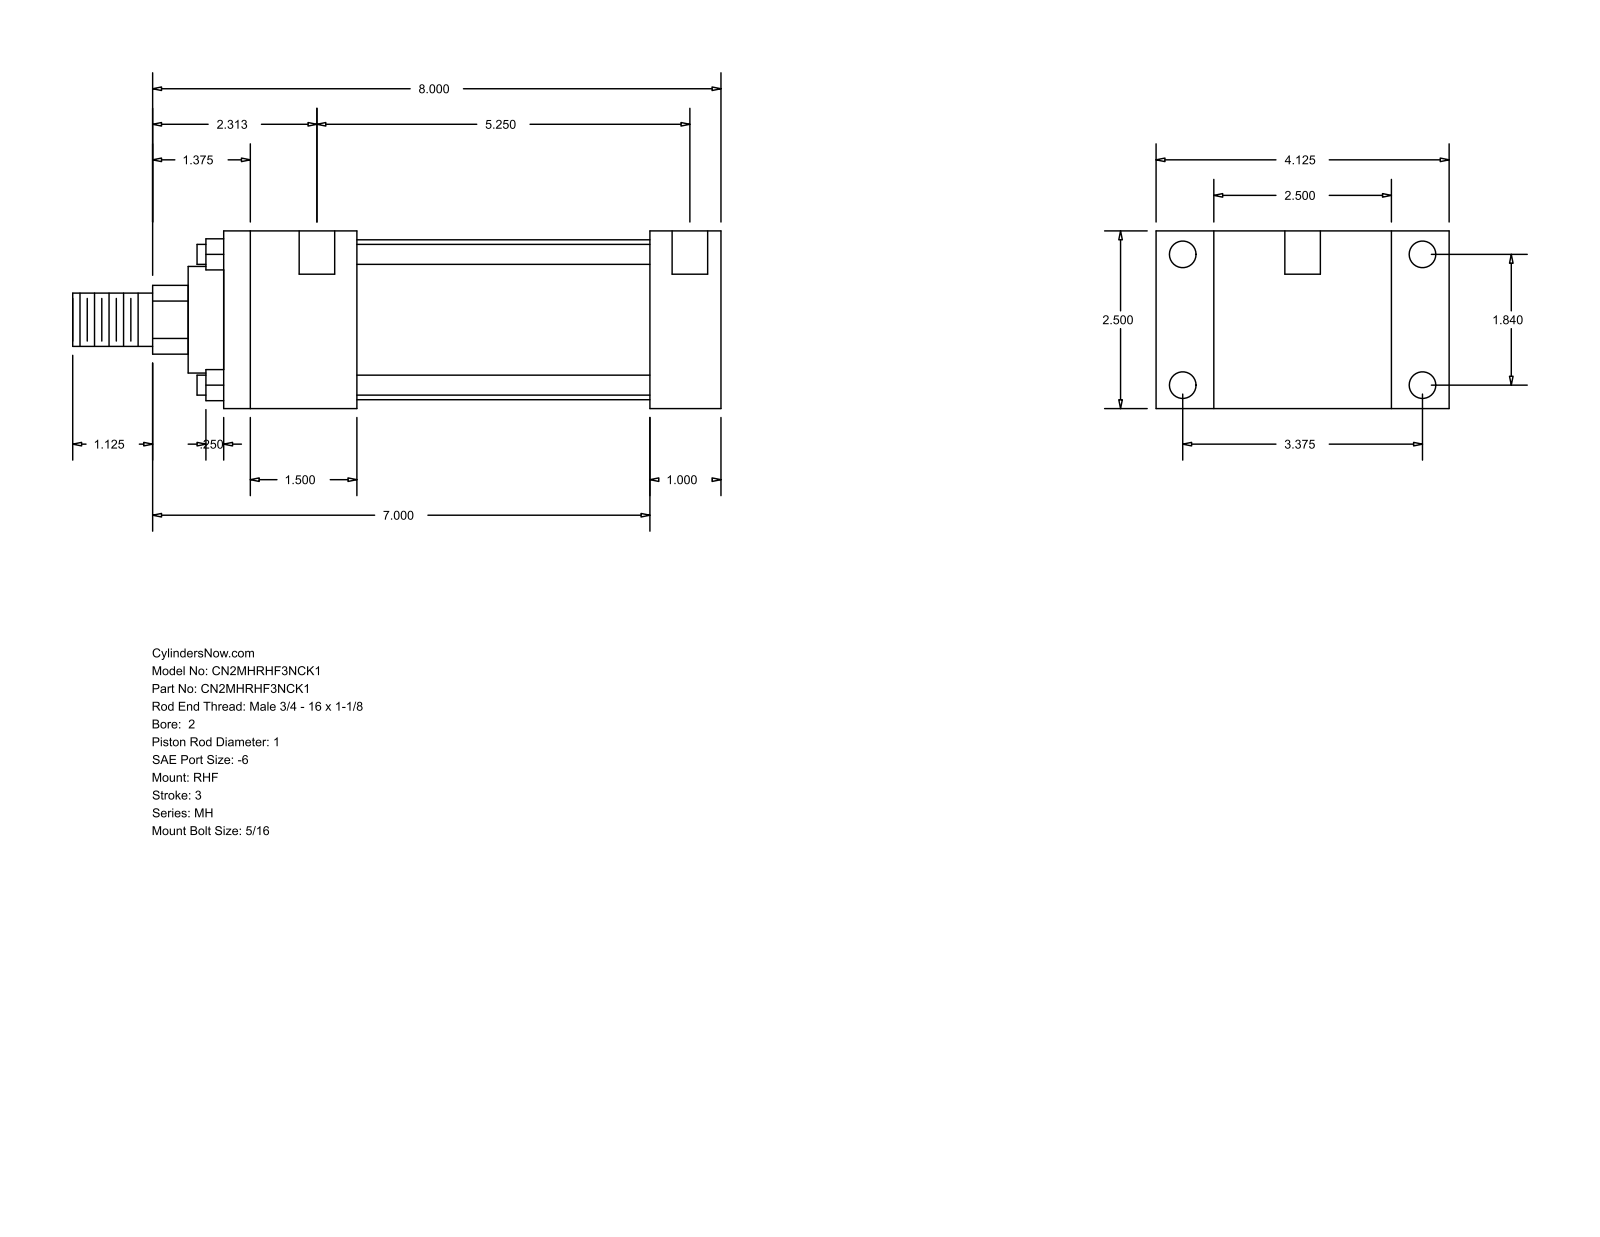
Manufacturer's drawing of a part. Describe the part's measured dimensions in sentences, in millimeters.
The part is named "MH_RHF__0200_1". Its 3-D file was written by "GSSL Pune (CONFIG_CONTROL_DESIGN)". It is 0 solids with 88 faces: 60 planar, 28 cylindrical and 0 other. Overall it measures 231.78 by 104.78 by 63.5 millimeters. Round holes: 4 of diameter 5.56, 4 of diameter 9.53, 2 of diameter 12.7. Round bosses or shafts: 4 of diameter 7.14, 1 of diameter 57.15, 1 of diameter 38.1, 1 of diameter 25.4, 1 of diameter 19.05. Partial cylindrical surfaces (rounded edges, fillets, slot ends): 1 of radius 12.29. The main face-to-face distances are 63.5, 25.4, 20.64, 84.14, 177.8, 152.4, 104.78, 104.77, 47.63, 130.17. The hole center spacings are 46.74, 85.72, 97.63, 141.28, 3.17, 4.76, 133.35, 136.52.
